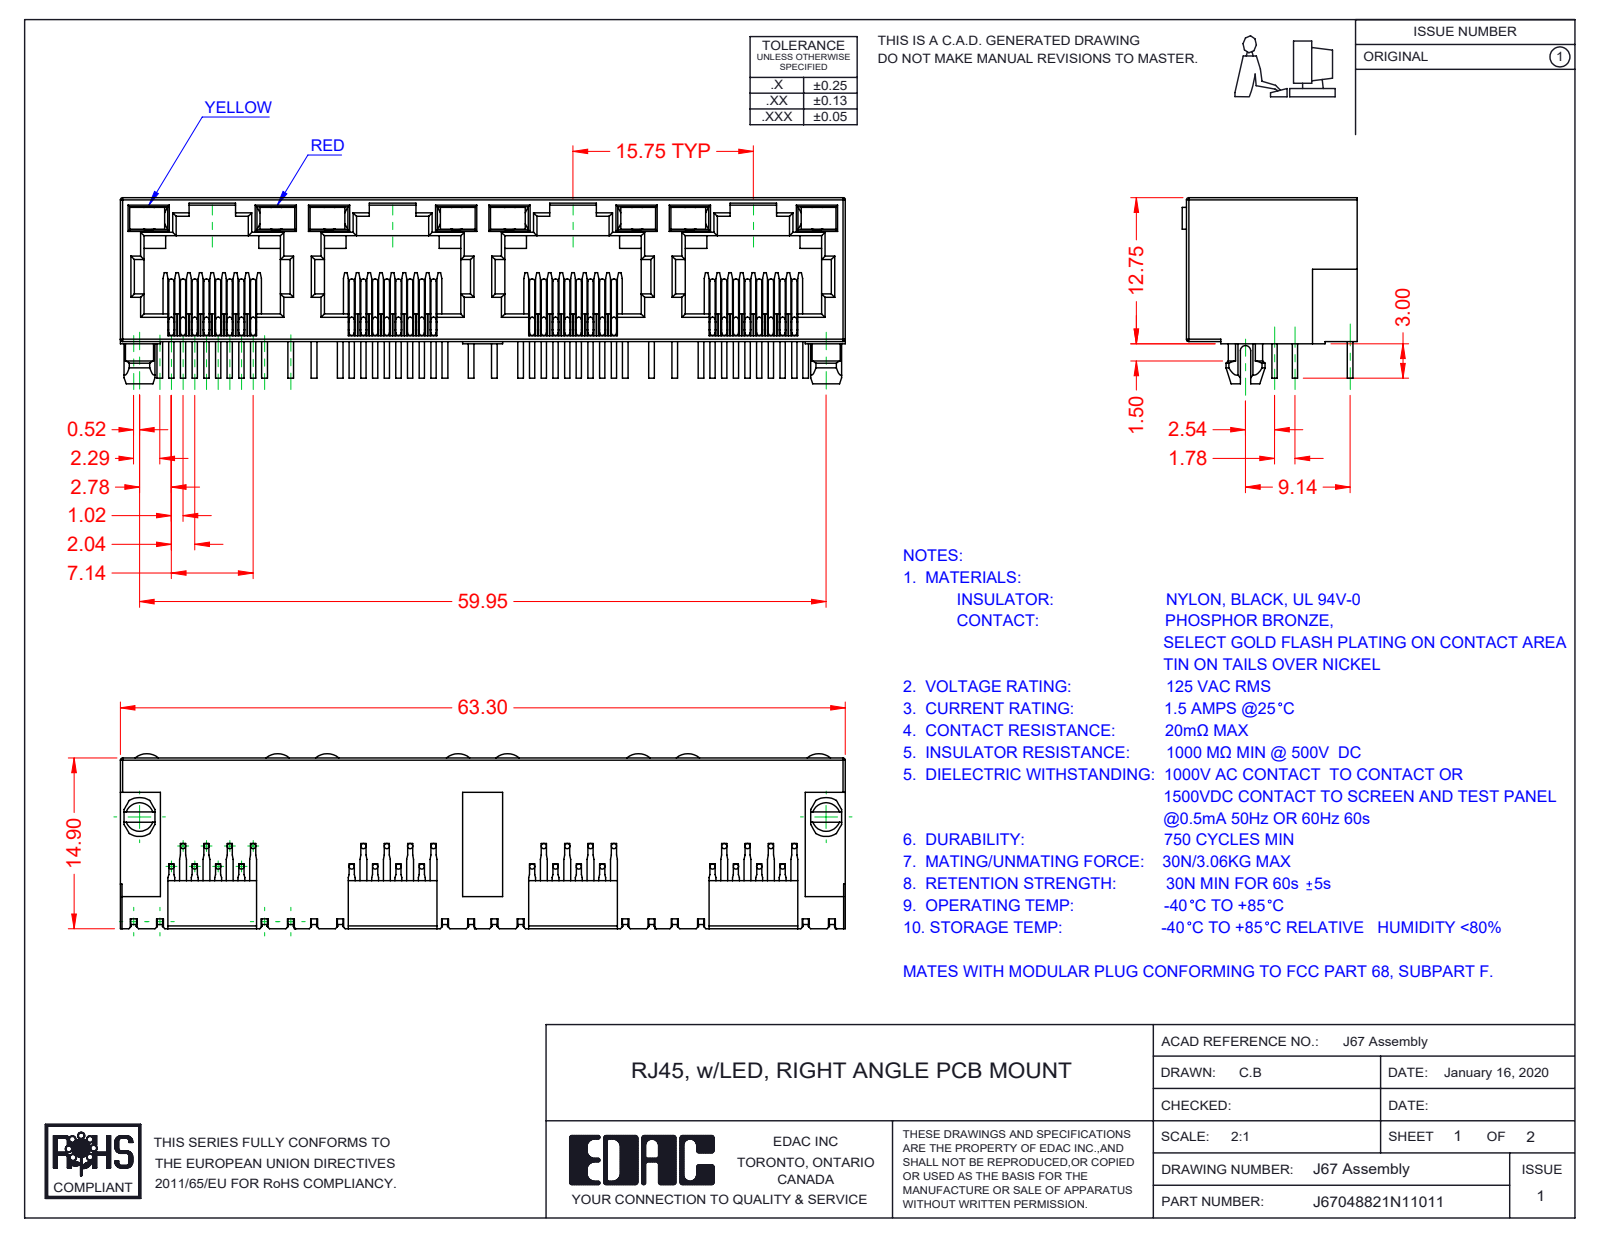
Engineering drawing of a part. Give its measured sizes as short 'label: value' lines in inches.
name: 67 Contacts; 67 Insulator; 67 LED RH_2-Red; 67 LED LH_1-Yellow (+1 more)
written by: SolidWorks 2016 (CONFIG_CONTROL_DESIGN)
unit: in
bodies: 41 solids, 2465 faces (1781 planar, 476 cylindrical, 208 other)
size: 2.492 × 0.64 × 0.602
volume: 0.315 in³; area: 17.94 in²
bosses: 96× ⌀0.018
rounds: 66× R0.008, 29× R0.012, 9× R0.018, 8× R0.061, 2× R0.059, 2× R0.067, 1× R0.014, 1× R0.039
face distances: 0.02, 0.494, 0.074, 0.035, 0.394, 0.62, 0.039, 0.055, 0.433, 0.468
